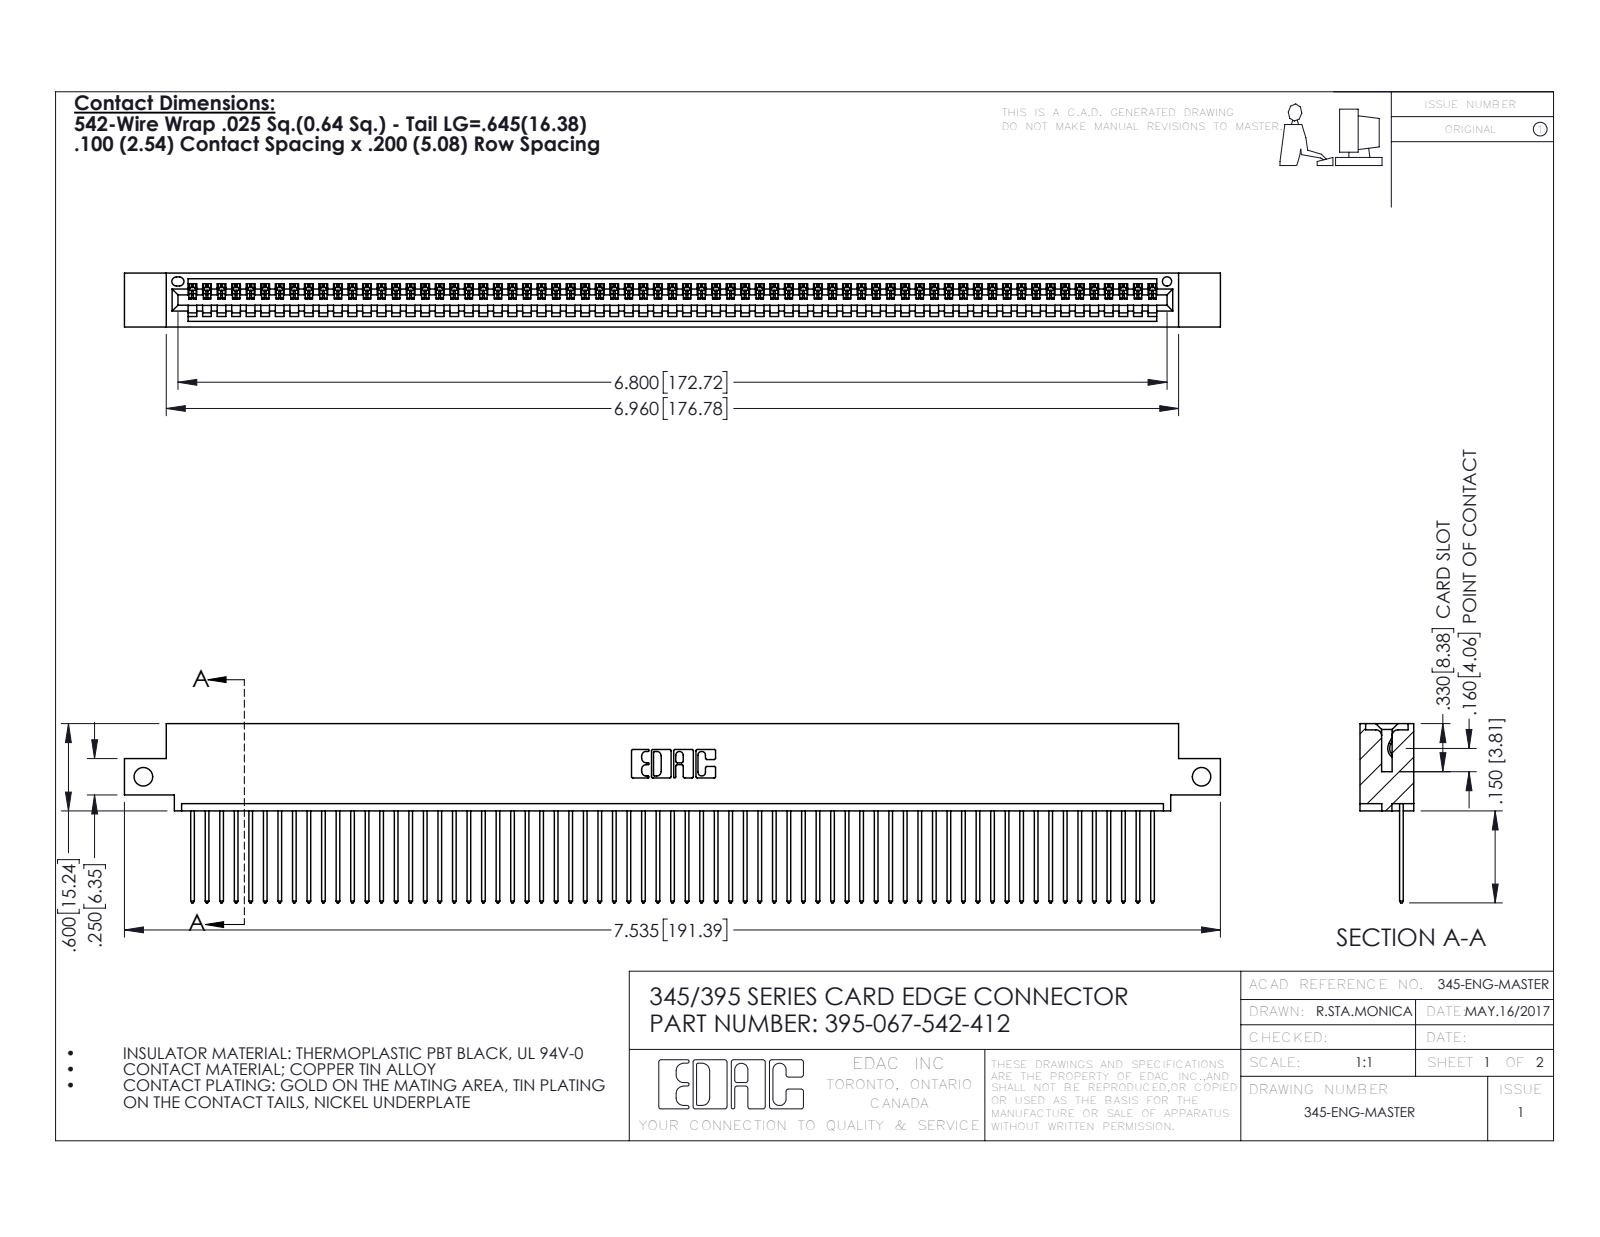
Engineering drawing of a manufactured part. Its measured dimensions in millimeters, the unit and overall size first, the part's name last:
Units: millimetres
Overall size (bounding box): 191.4 × 31.3 × 9.4
Round holes (diameter × count): ⌀3.3 ×2, ⌀1.6 ×1
Partial cylindrical surfaces — rounded edges, fillets, slot ends (radius × count): R0.2 ×134, R0.3 ×134, R0.3 ×22, R0.2 ×6, R0.8 ×6, R0.7 ×3, R0.8 ×2, R1 ×2
Main face-to-face distances: 1.8, 7.6, 2.5, 6.9, 0.6, 9.4, 5.1, 5.7, 3.8, 1.8
Hole centre spacings: 184.8
Volume: 18 370 mm³ · Surface area: 25 640 mm²
Bodies: 68 solids, 4016 faces (2764 planar, 1252 cylindrical, 0 other)
Part name (STEP PRODUCT): 395-067-542-412; 345-292-001_345-293-142; 345 Part_0.110 Offset - Side Mount
STEP written by: SolidWorks 2016 (CONFIG_CONTROL_DESIGN)
